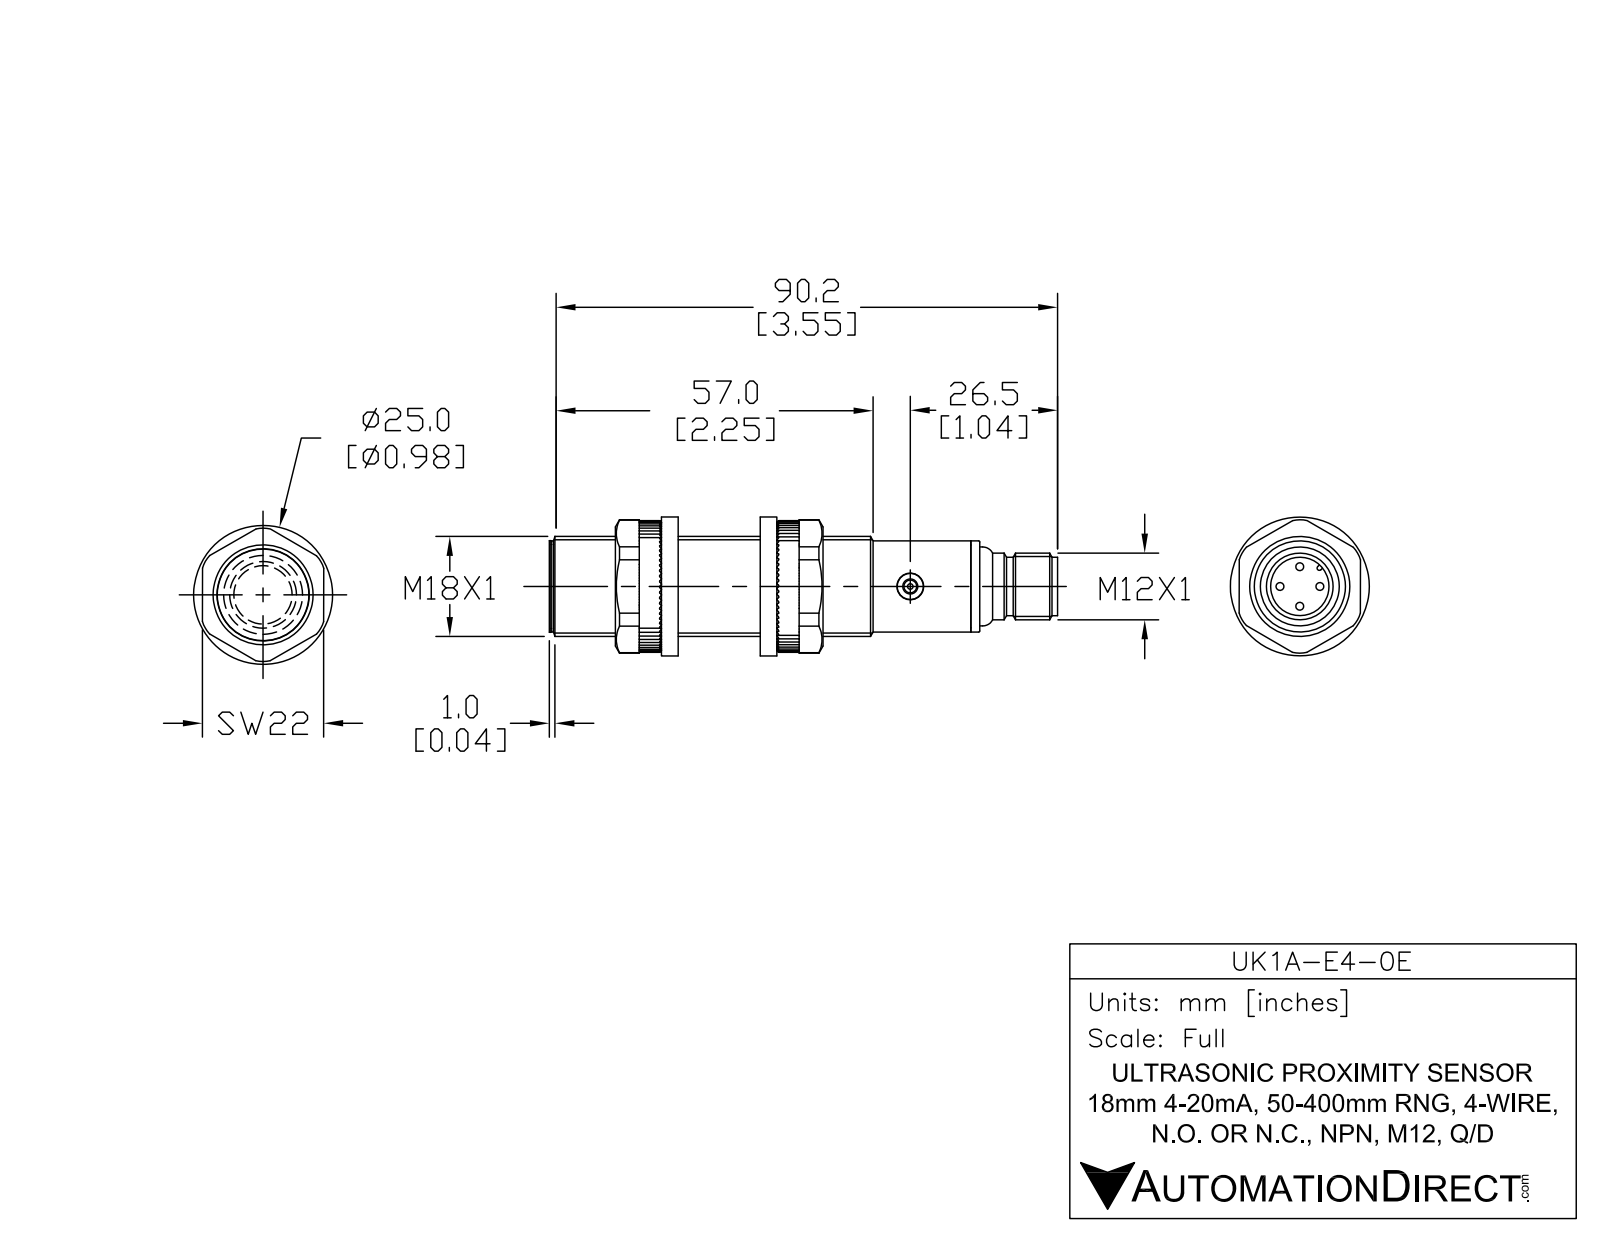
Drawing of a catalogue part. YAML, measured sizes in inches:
part_name: "UK1A-E4-0E"
step_written_by: "SolidWorks 2017 (AUTOMOTIVE_DESIGN)"
units: inches
bodies: {solids: 6, faces: 106, planar: 21, cylindrical: 48, other: 37}
overall_size: [3.606, 0.709, 0.709]
volume: 1.202
surface_area: 10.68
round_holes:
  - {diameter: 0.106, count: 1}
  - {diameter: 0.185, count: 1}
  - {diameter: 0.276, count: 1}
  - {diameter: 0.327, count: 1}
  - {diameter: 0.374, count: 1}
round_bosses_or_shafts:
  - {diameter: 0.039, count: 4}
  - {diameter: 0.709, count: 1}
  - {diameter: 0.654, count: 1}
  - {diameter: 0.646, count: 1}
  - {diameter: 0.622, count: 1}
  - {diameter: 0.559, count: 1}
  - {diameter: 0.472, count: 1}
  - {diameter: 0.413, count: 1}
partial_cylinders:
  - {radius: 0.024, count: 1}
face_to_face_distances: [2.957, 0.039, 2.996, 0.037, 2.994, 0.043, 0.157, 3.055, 3.053, 3.016]
